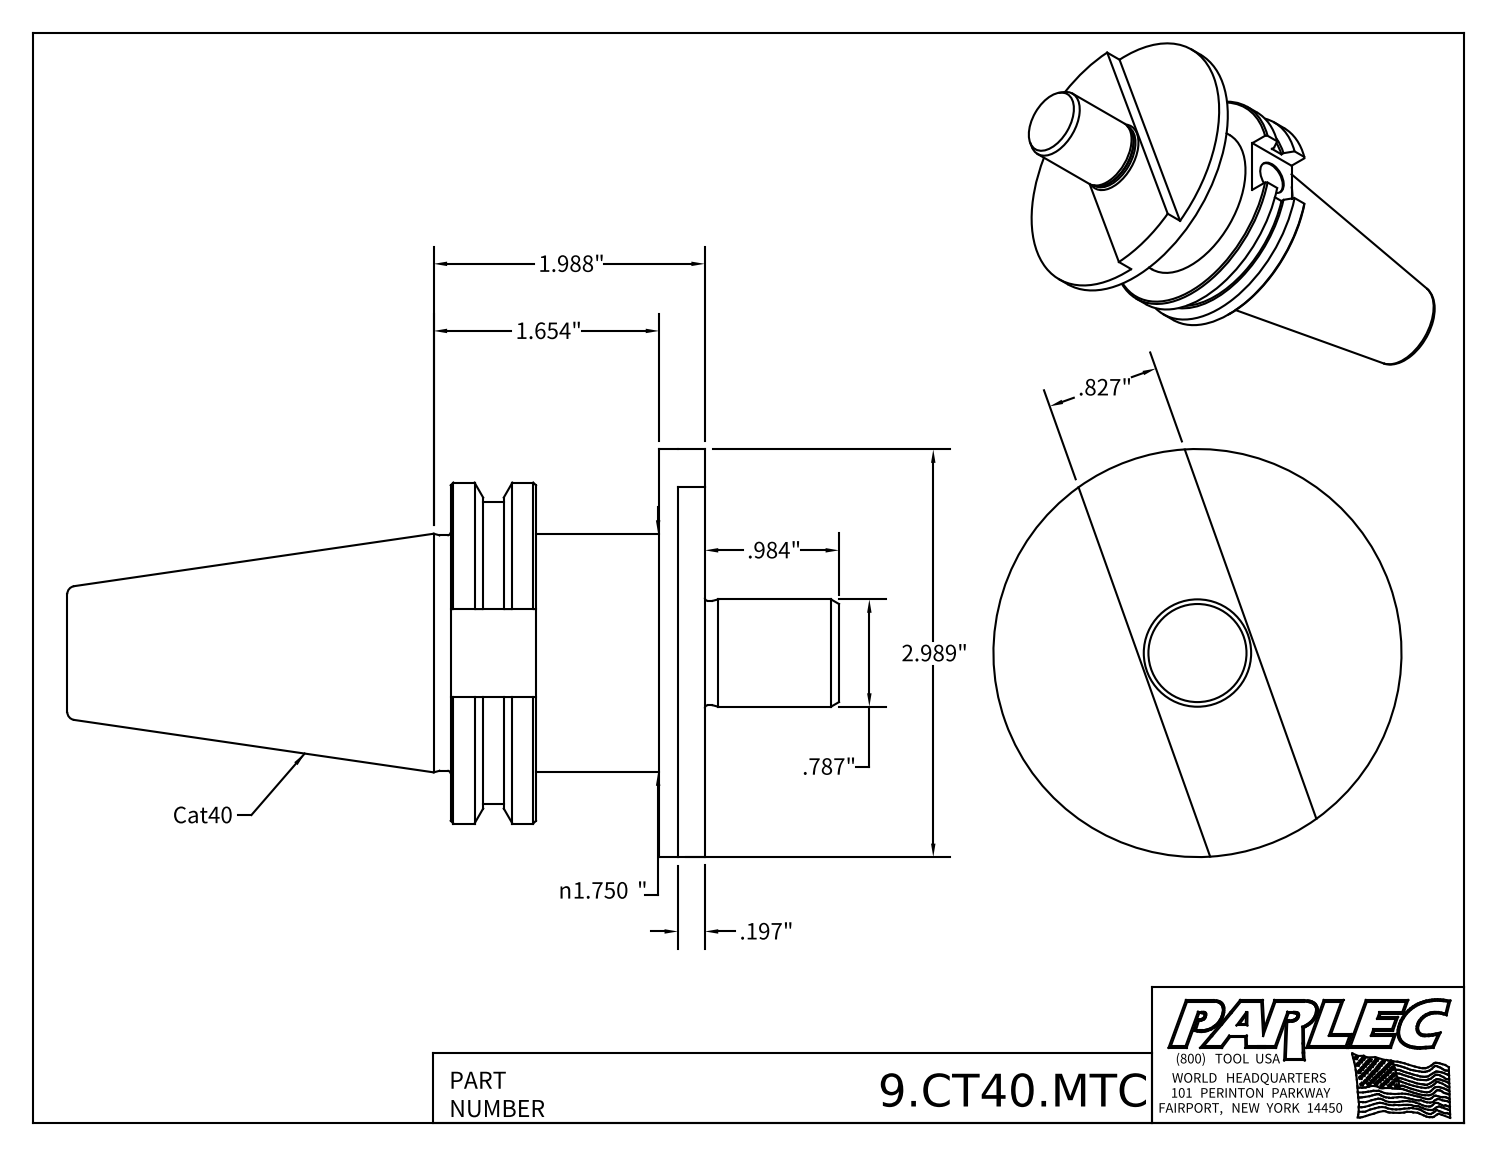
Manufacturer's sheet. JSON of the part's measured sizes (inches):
{"part_name": "9.CT40.MTC; 9_SK_44_2 (Cat40, MTC)", "step_written_by": "Autodesk Inventor 2022 (AUTOMOTIVE_DESIGN)", "units": "inches", "bodies": {"solids": 1, "faces": 58, "planar": 23, "cylindrical": 15, "other": 20}, "overall_size": [5.659, 2.992, 2.992], "volume_in3": 10.57, "surface_area_in2": 48.68, "round_holes": [[0.375, 1], [0.527, 1], [0.641, 1], [0.661, 1]], "round_bosses_or_shafts": [[2.992, 1], [2.5, 1], [2.219, 1], [1.75, 1], [1.726, 1], [0.787, 1], [0.764, 1]], "face_to_face_distances": [0.138, 1.041, 0.904, 0.197, 0.335, 1.238, 1.863, 1.666, 1.528, 0.625]}
